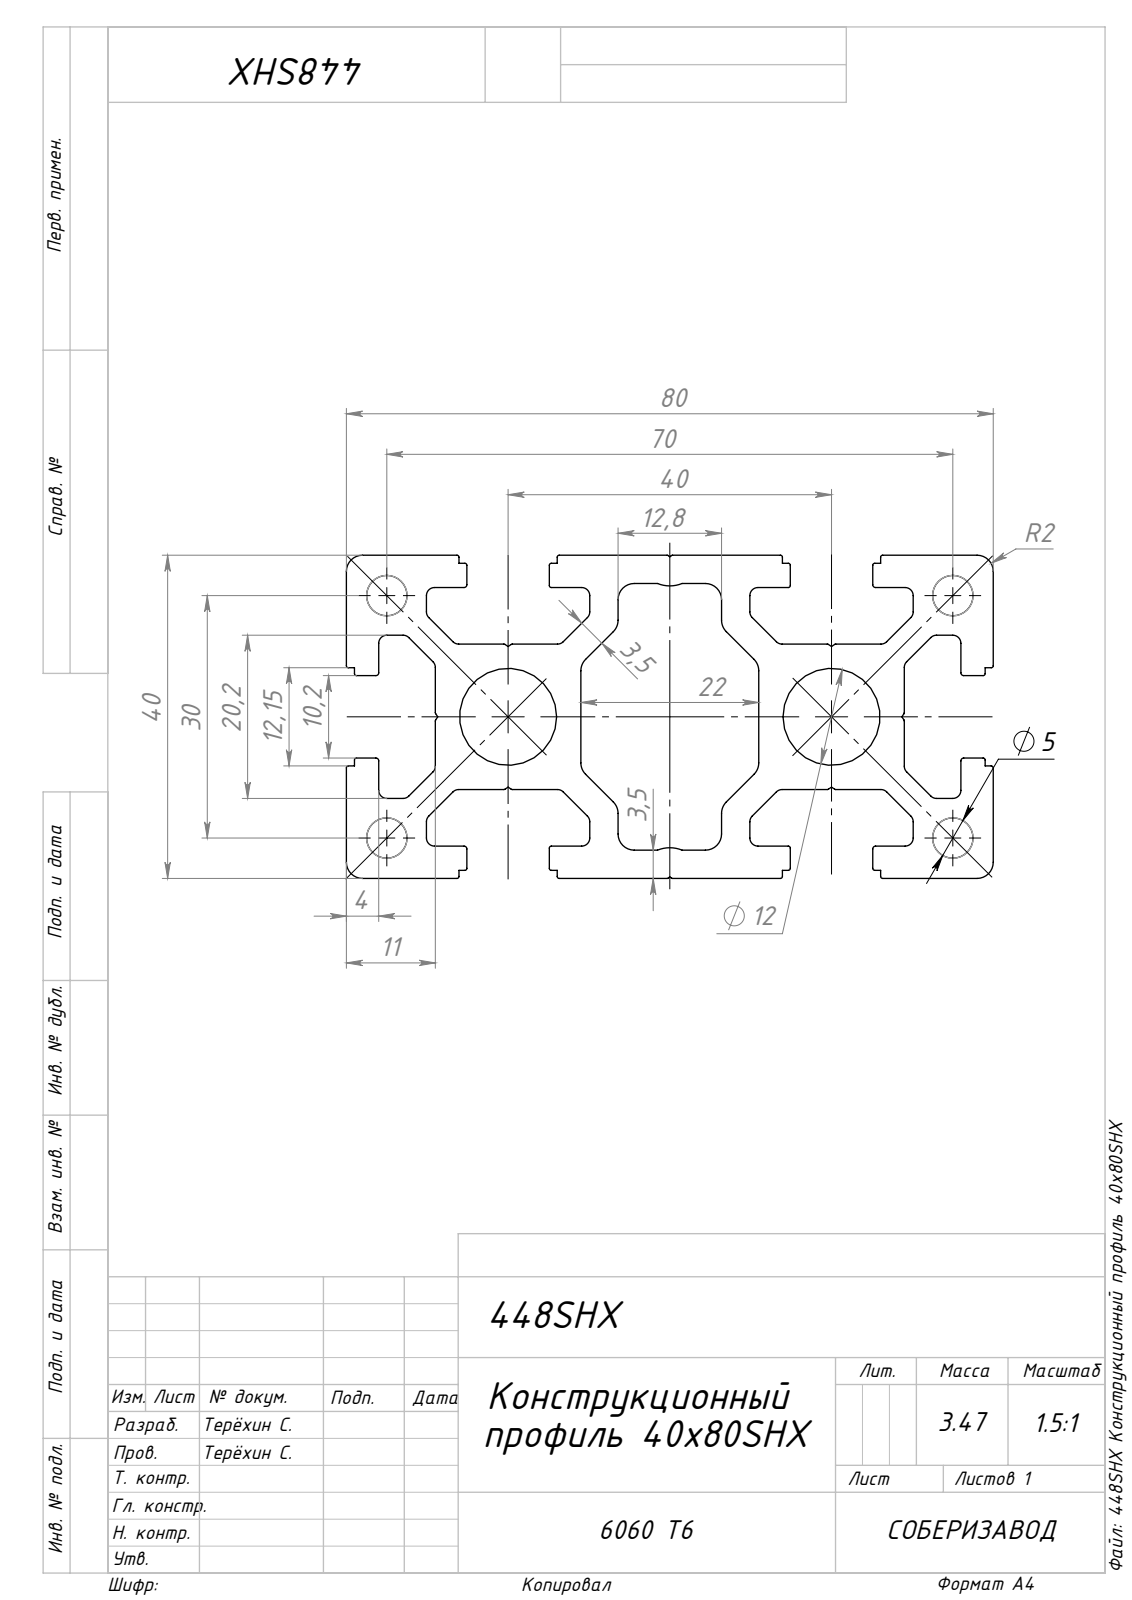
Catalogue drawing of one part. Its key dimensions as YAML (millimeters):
part_name: "448SHX Конструкционный профиль 40х80SH_00; 448SHX Конструкционный профиль 40х80SH"
step_written_by: "SolidWorks 2025 (CONFIG_CONTROL_DESIGN)"
units: millimeters
bodies: {solids: 1, faces: 254, planar: 128, cylindrical: 126, other: 0}
overall_size: [1000, 80, 40]
volume: 1285000
surface_area: 690395
round_holes:
  - {diameter: 5, count: 4}
  - {diameter: 12, count: 2}
partial_cylinders:
  - {radius: 0.25, count: 44}
  - {radius: 1, count: 36}
  - {radius: 2, count: 16}
  - {radius: 0.35, count: 8}
  - {radius: 4, count: 2}
face_to_face_distances: [40, 29, 11, 3.5, 18, 4, 7, 25, 28.28, 36]
hole_center_spacings: [21.21, 57.01, 30, 70, 76.16, 40]
